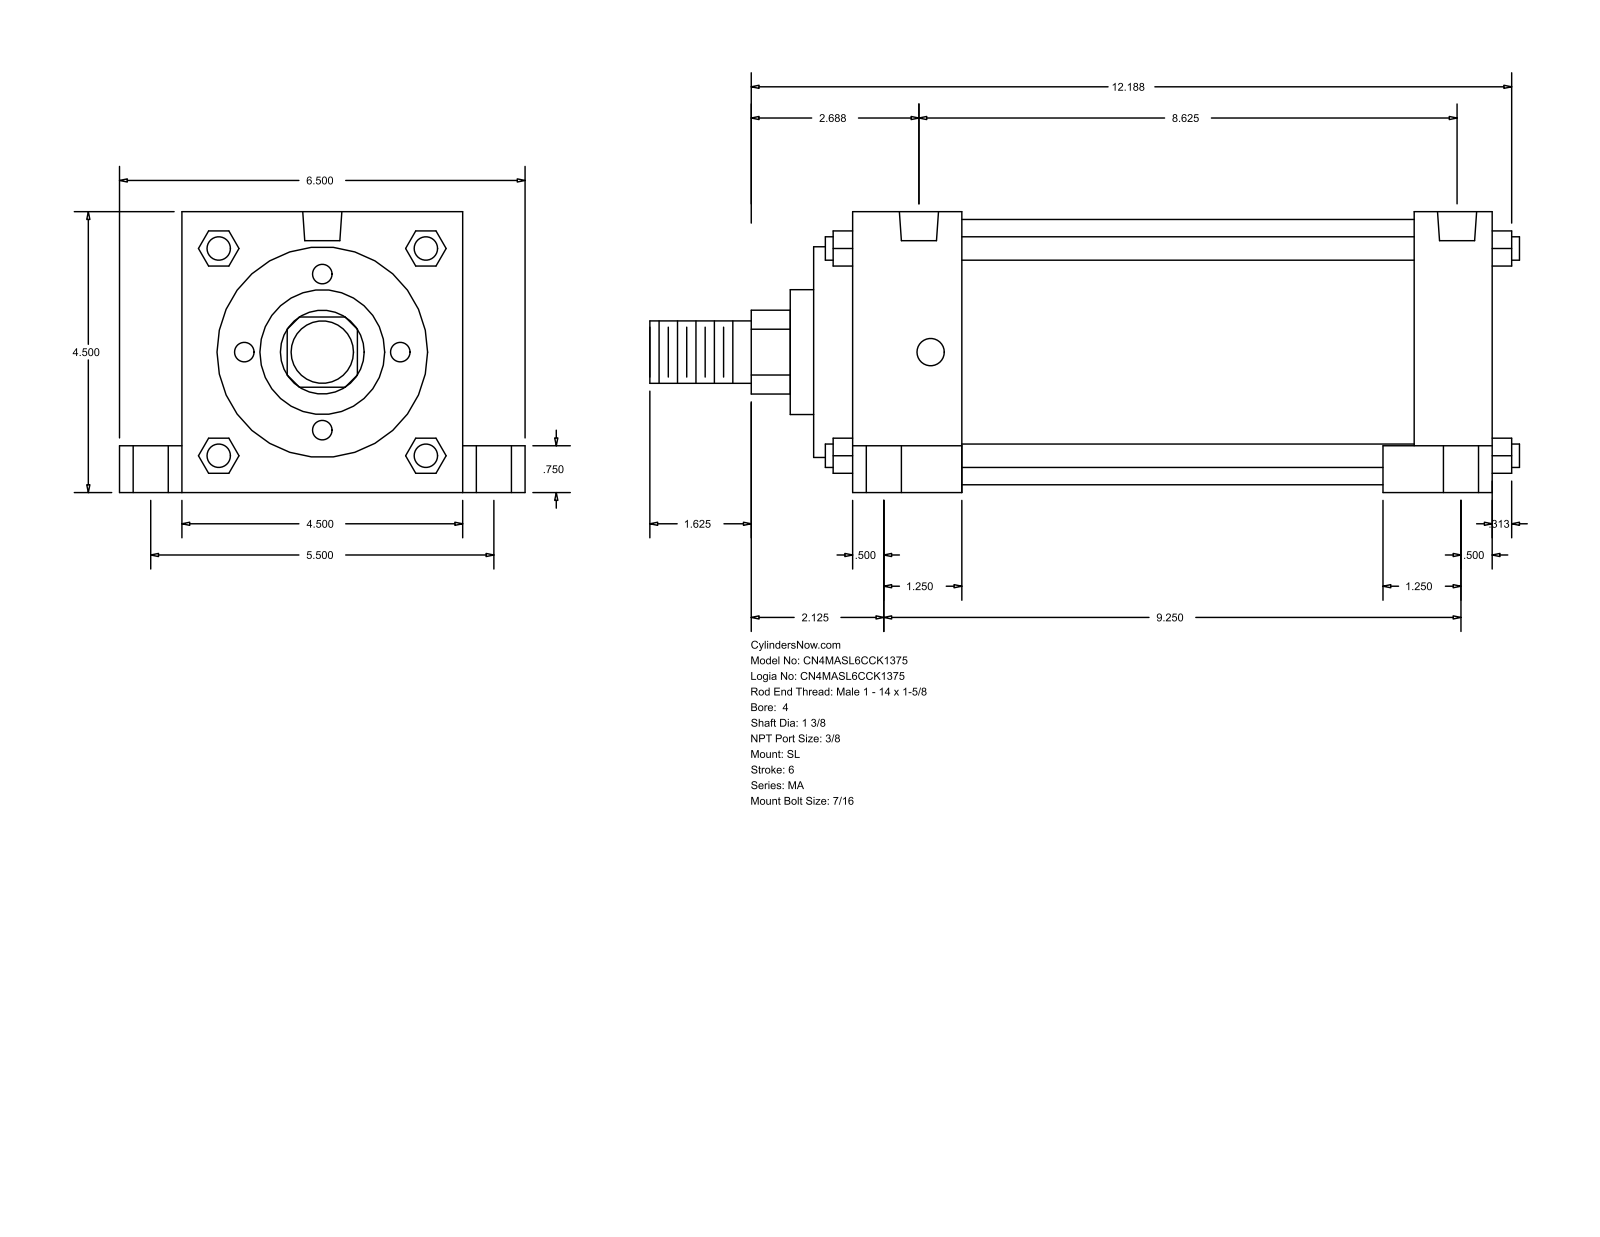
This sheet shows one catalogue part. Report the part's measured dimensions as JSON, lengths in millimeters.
{"part_name": "MA_SL__0400_1.375", "step_written_by": "GSSL Pune (CONFIG_CONTROL_DESIGN)", "units": "millimeters", "bodies": {"solids": 0, "faces": 150, "planar": 113, "cylindrical": 37, "other": 0}, "overall_size": [354.01, 165.1, 114.3], "round_holes": [[11.11, 4], [14.29, 4], [20.64, 4], [15.93, 2]], "round_bosses_or_shafts": [[9.53, 4], [107.95, 1], [85.72, 1], [50.8, 1], [34.92, 1], [25.4, 1]], "partial_cylinders_radius": [[17.06, 1]], "face_to_face_distances": [114.3, 260.35, 276.22, 15.87, 60.32, 44.45, 215.9, 244.48, 228.61, 184.16], "hole_center_spacings": [4.77, 69.87, 70.14, 71.29, 72.4, 139.7, 209.54, 214.31]}
